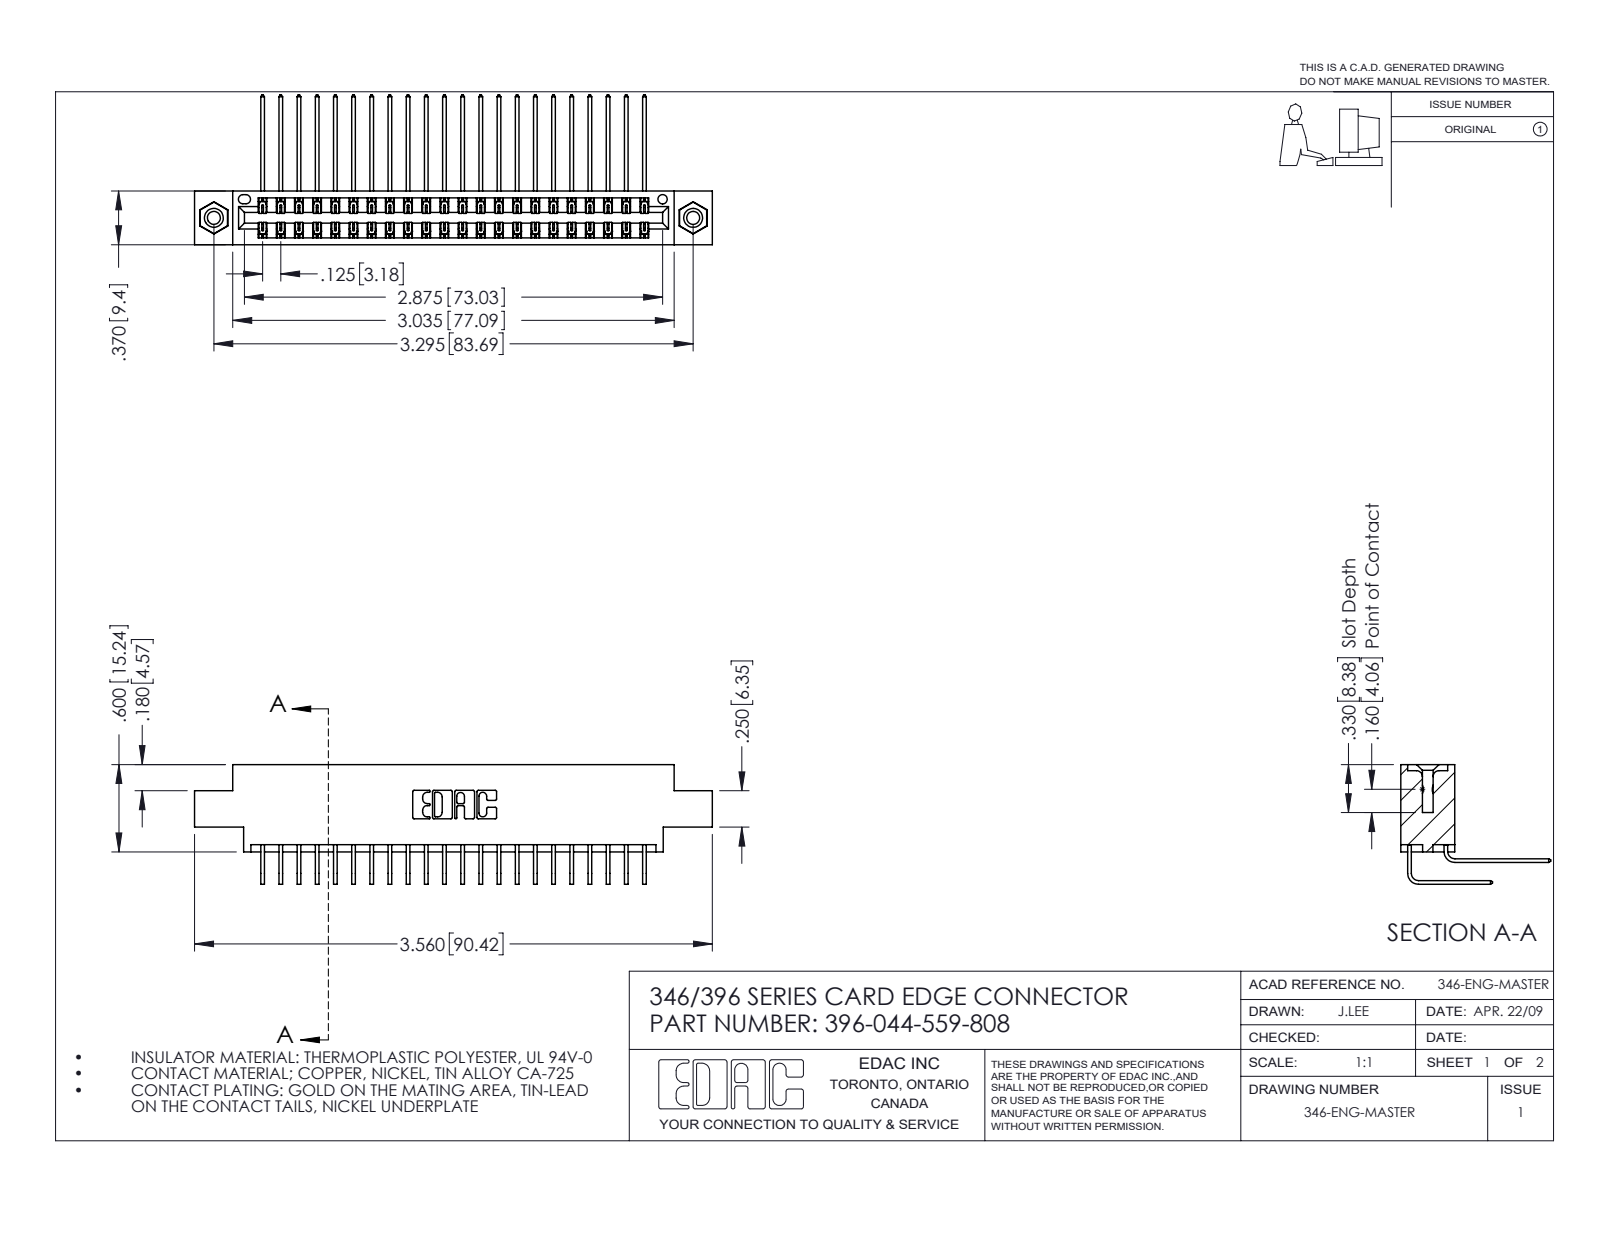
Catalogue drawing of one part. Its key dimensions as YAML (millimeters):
part_name: "345-292-001_559 Tail - 2; 345-292-001_558 559 Tail - 1; 396-044-559-808; 346 Part_0.170 Offset - 0.156 Dia-TI (+1 more)"
step_written_by: "SolidWorks 2016 (CONFIG_CONTROL_DESIGN)"
units: millimeters
bodies: {solids: 47, faces: 2562, planar: 1740, cylindrical: 806, other: 16}
overall_size: [90.4, 26.2, 20.9]
volume: 8750
surface_area: 13140
round_holes:
  - {diameter: 2.3, count: 2}
  - {diameter: 3.2, count: 2}
  - {diameter: 4, count: 2}
  - {diameter: 1.6, count: 1}
round_bosses_or_shafts:
  - {diameter: 3.9, count: 2}
partial_cylinders:
  - {radius: 0.2, count: 66}
  - {radius: 0.3, count: 22}
  - {radius: 0.2, count: 6}
  - {radius: 0.8, count: 6}
  - {radius: 0.7, count: 3}
  - {radius: 0.4, count: 2}
  - {radius: 0.6, count: 2}
  - {radius: 0.6, count: 2}
face_to_face_distances: [1.2, 8.2, 0.6, 9.4, 6.4, 1.8, 7.6, 7, 5.6, 3.8]
hole_center_spacings: [6.2, 78.4, 83.7]
